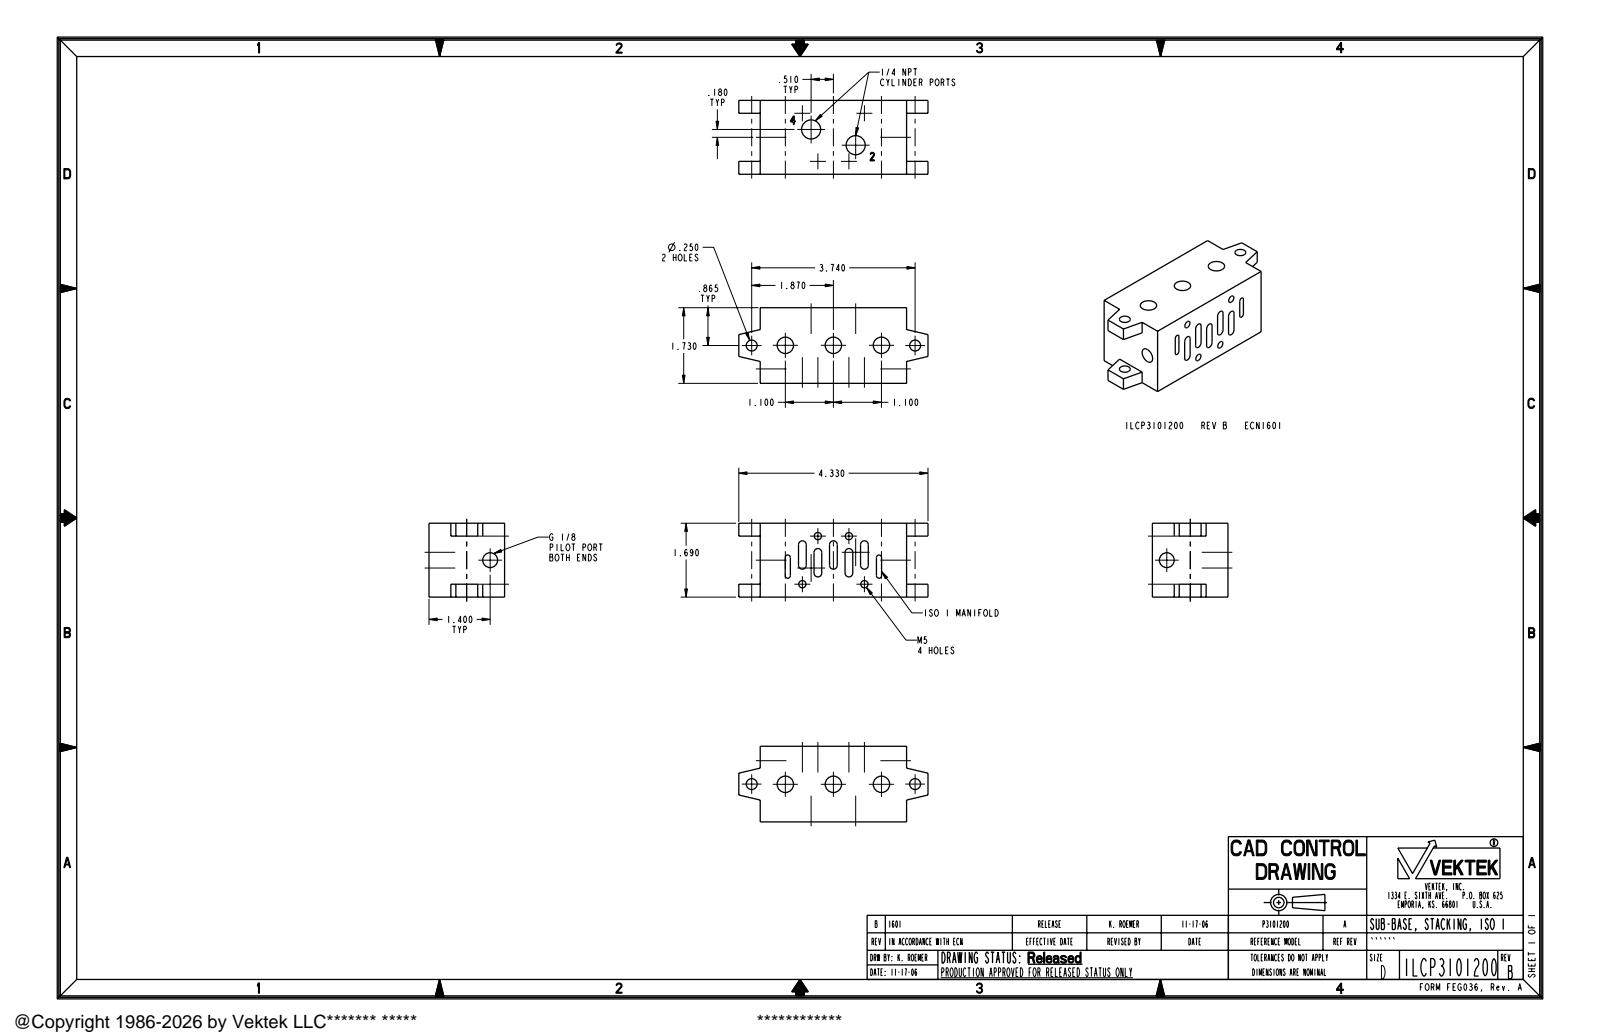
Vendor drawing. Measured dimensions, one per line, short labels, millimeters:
name: ILCP3101200
written by: PRO/ENGINEER BY PARAMETRIC TECHNOLOGY CORPORATION, 2005180 (AUTOMOTIVE_DESIGN_CC2)
unit: mm
bodies: 1 solid, 140 faces (96 planar, 44 cylindrical, 0 other)
size: 110 × 43.9 × 42.9
volume: 148 800 mm³; area: 28 350 mm²
holes: 4× ⌀4.2, 3× ⌀9.5, 2× ⌀6.4, 2× ⌀11.1, 1× ⌀8.6
rounds: 10× R2.3, 4× R1.5
face distances: 42.9, 43.9, 85.1, 6.4, 9, 37.6, 12.7, 35.4, 7.5, 7.5
hole spacings: 19.6, 27.9, 29.4, 38.9, 47.5, 75.4, 10.2, 10.7
